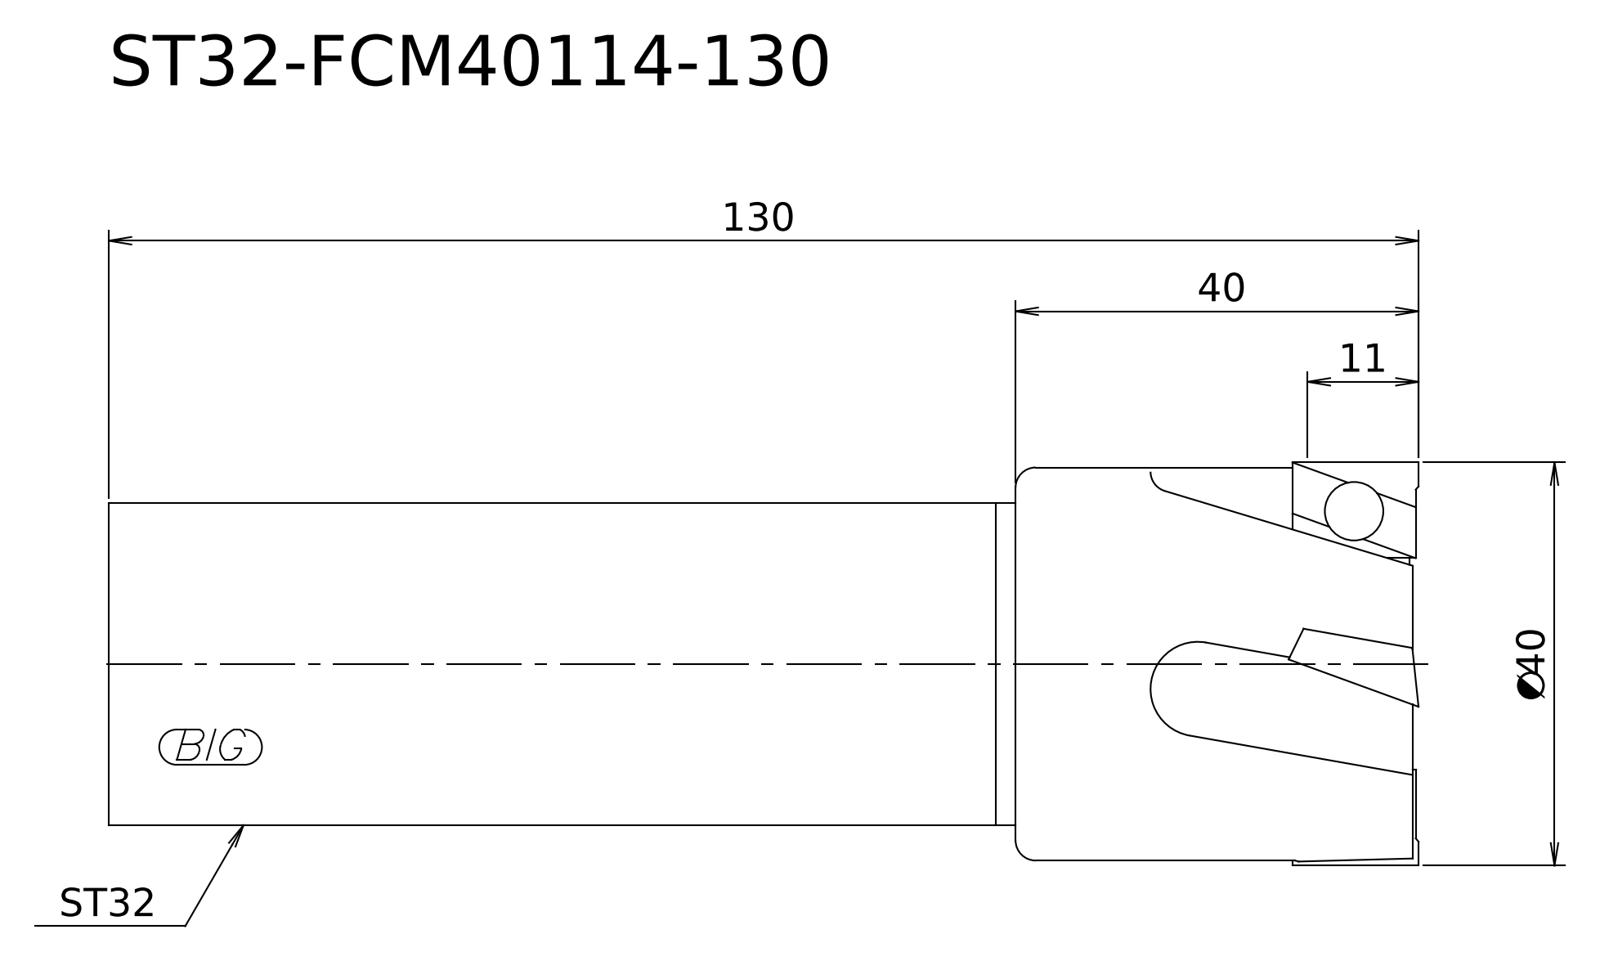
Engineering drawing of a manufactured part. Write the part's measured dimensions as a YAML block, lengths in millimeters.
step_written_by: "Kubotek KeyCreator V8.5.1 (14335) (CONFIG_CONTROL_DESIGN)"
units: millimeters
bodies: {solids: 1, faces: 7, planar: 4, cylindrical: 3, other: 0}
overall_size: [130, 40, 40]
volume: 120942
surface_area: 16501
round_bosses_or_shafts:
  - {diameter: 40, count: 1}
  - {diameter: 39, count: 1}
  - {diameter: 32, count: 1}
face_to_face_distances: [130, 40, 90, 12.52, 27.48, 117.48]
